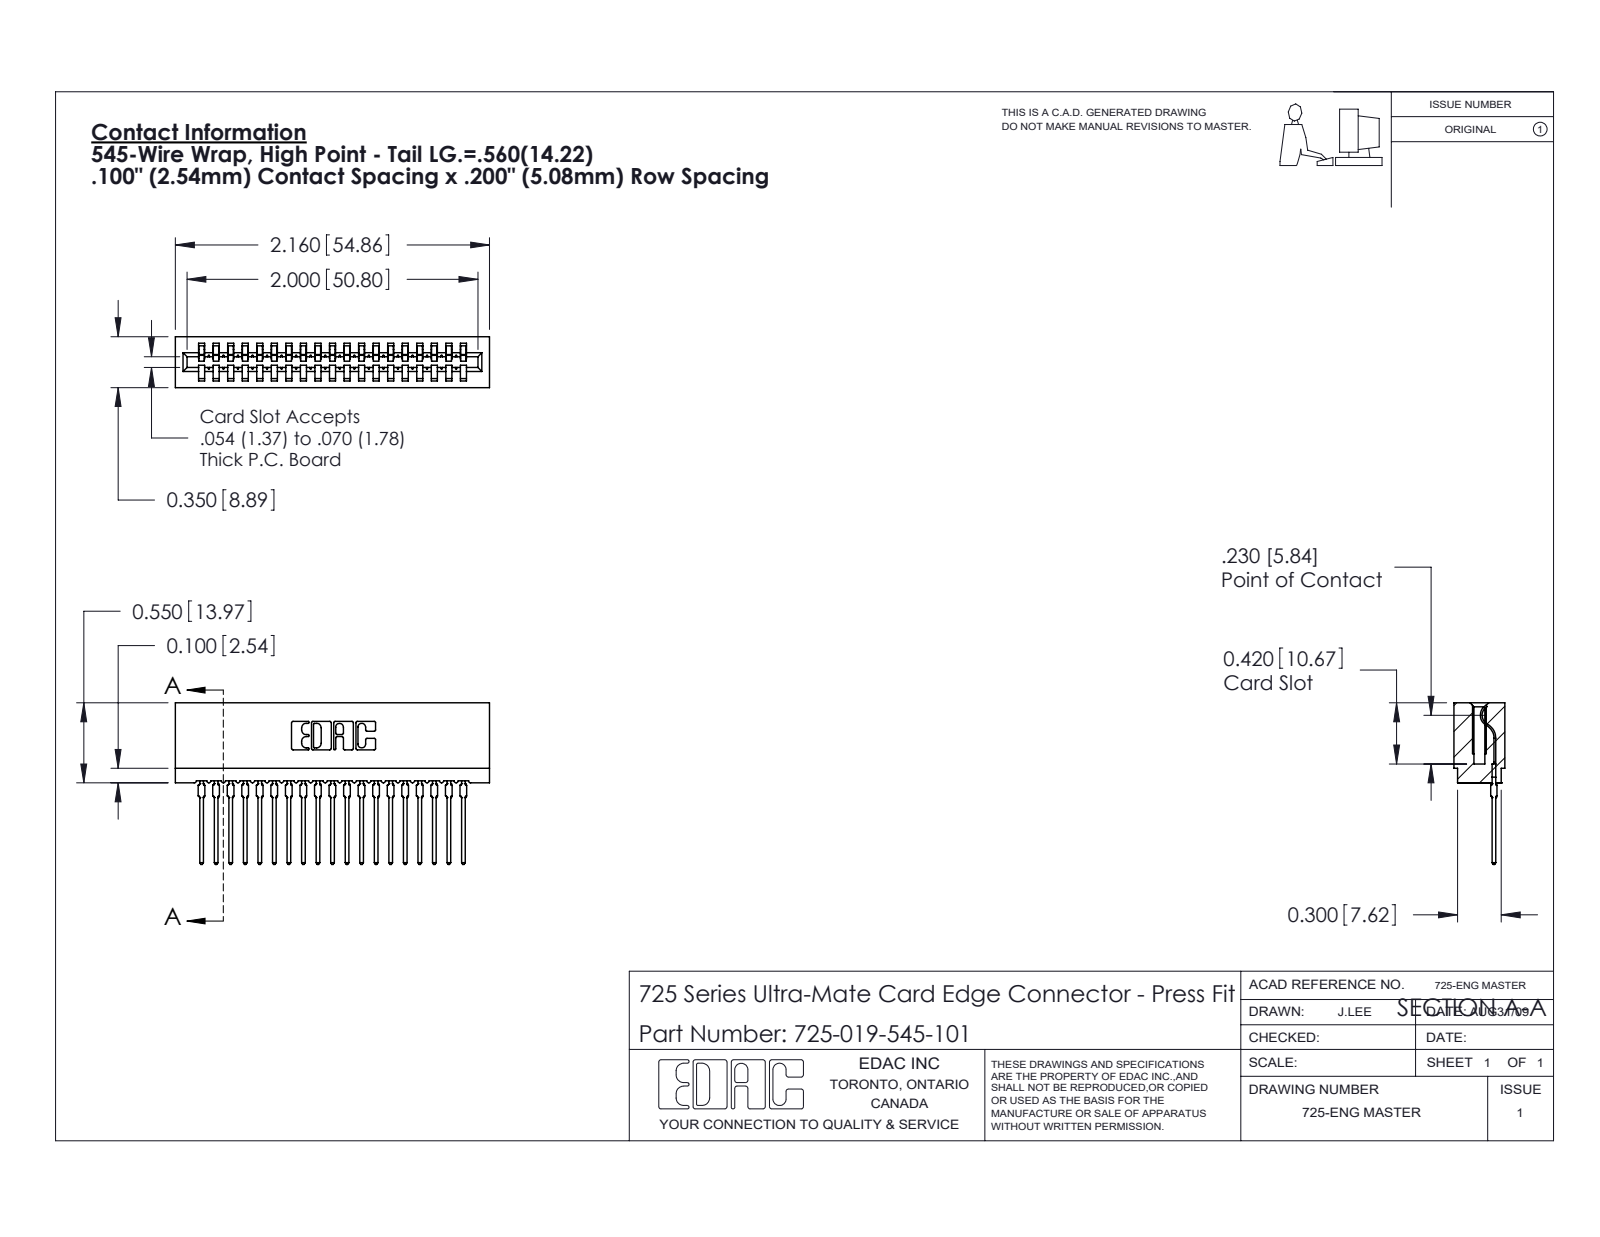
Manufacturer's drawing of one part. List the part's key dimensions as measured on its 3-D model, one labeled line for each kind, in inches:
Part name (STEP PRODUCT): 725 Part_Insulator Option - 01; 725-019-545-101; 745-292-001_545
STEP written by: SolidWorks 2020 (CONFIG_CONTROL_DESIGN)
Units: inches
Bodies: 20 solids, 2223 faces (1328 planar, 401 cylindrical, 494 other)
Overall size (bounding box): 2.16 × 1.111 × 0.35
Volume: 0.265 in³ · Surface area: 12.76 in²
Partial cylindrical surfaces — rounded edges, fillets, slot ends (radius × count): R0.015 ×38, R0.021 ×38, R0.01 ×22, R0.007 ×6, R0.031 ×6, R0.005 ×4, R0.011 ×4, R0.026 ×3
Main face-to-face distances: 0.1, 0.2, 0.3, 0.4, 0.5, 0.6, 0.7, 0.8, 0.35, 0.9
